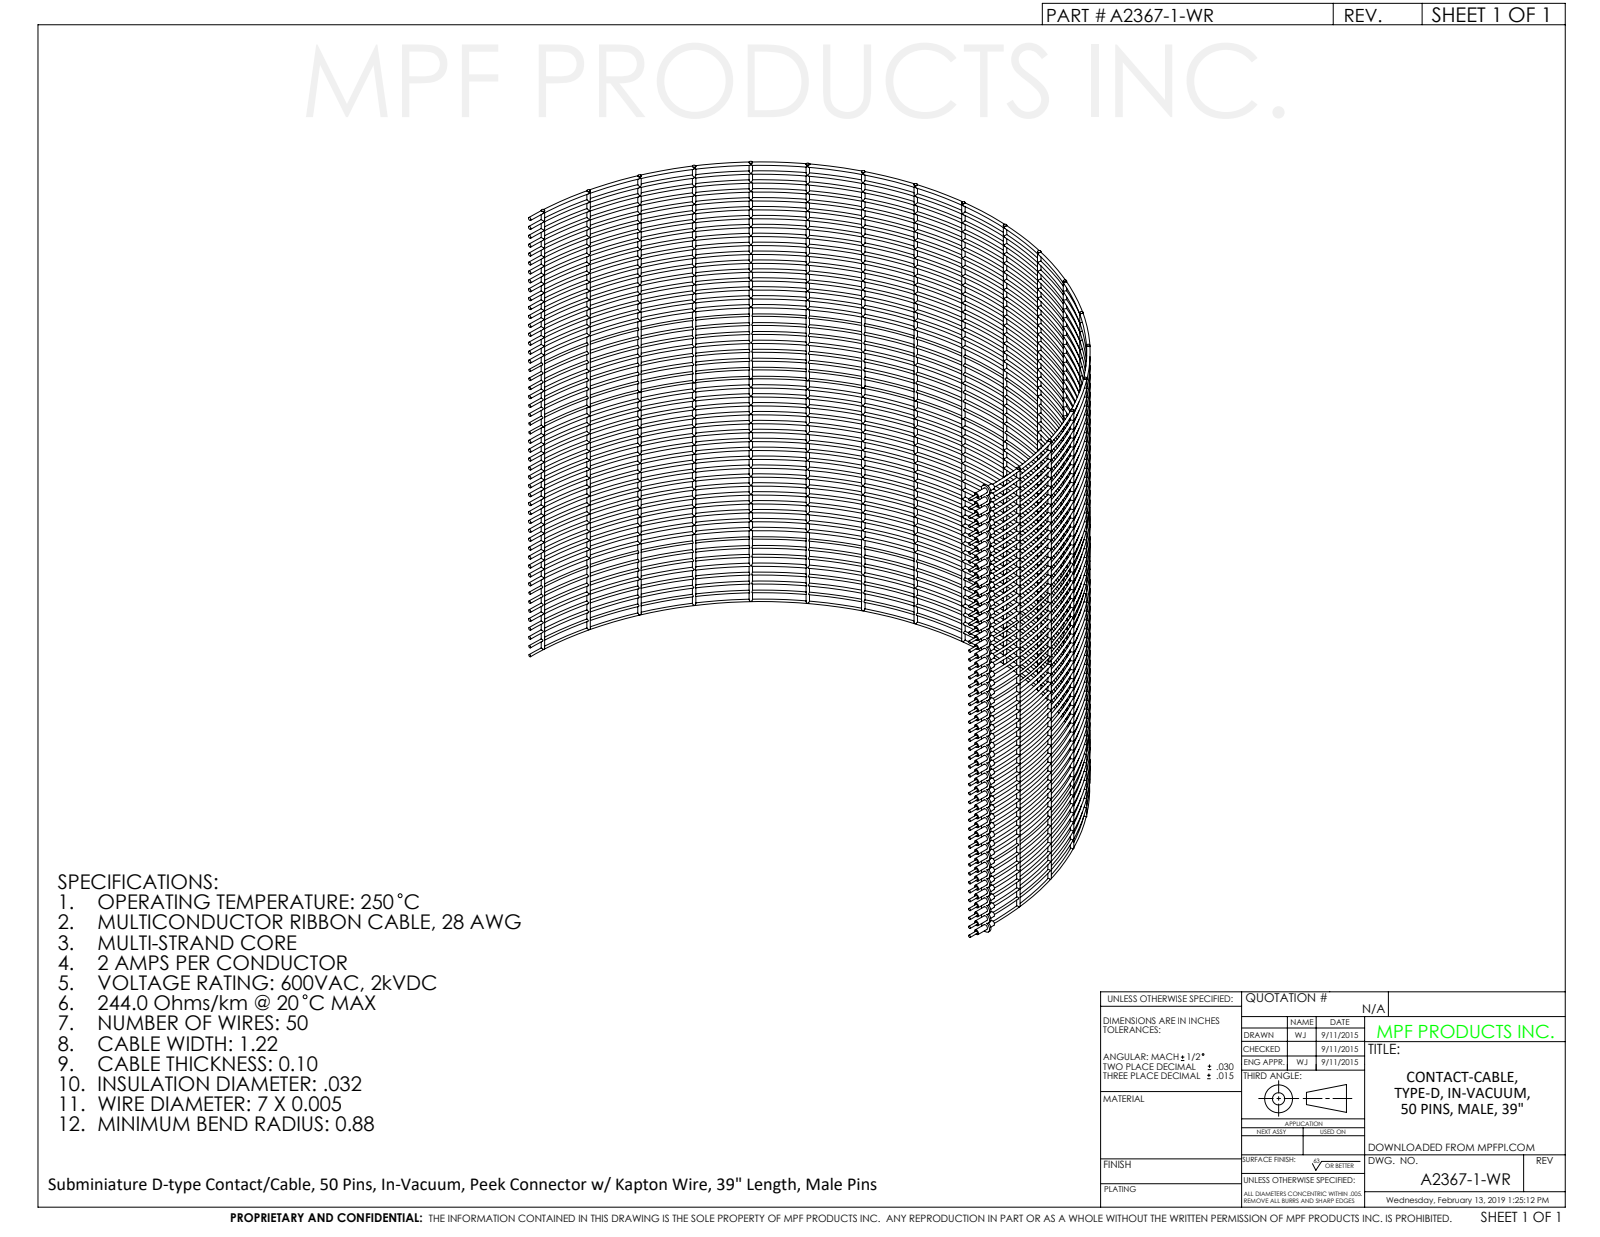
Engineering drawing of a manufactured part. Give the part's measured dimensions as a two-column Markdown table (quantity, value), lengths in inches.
| quantity | value |
| --- | --- |
| part name | A2367-1-WR |
| STEP written by | SolidWorks 2012 (CONFIG_CONTROL_DESIGN) |
| units | inches |
| bodies | 1 solid, 3930 faces (332 planar, 1706 cylindrical, 1892 other) |
| overall size | 6.069 × 5.005 × 3.315 |
| volume | 0.412 in³ |
| surface area | 52.44 in² |
| round bosses / shafts (diameter × count) | 0.05 × 50, 0.023 × 50, 0.105 × 48, 0.032 × 18 |
| partial cylindrical surfaces (radius × count) | 0.053 × 2 |
| main face-to-face distances | 0.018, 0.074, 0.091, 0.207, 0.134, 0.116, 0.298, 0.225, 0.207, 0.091 |
